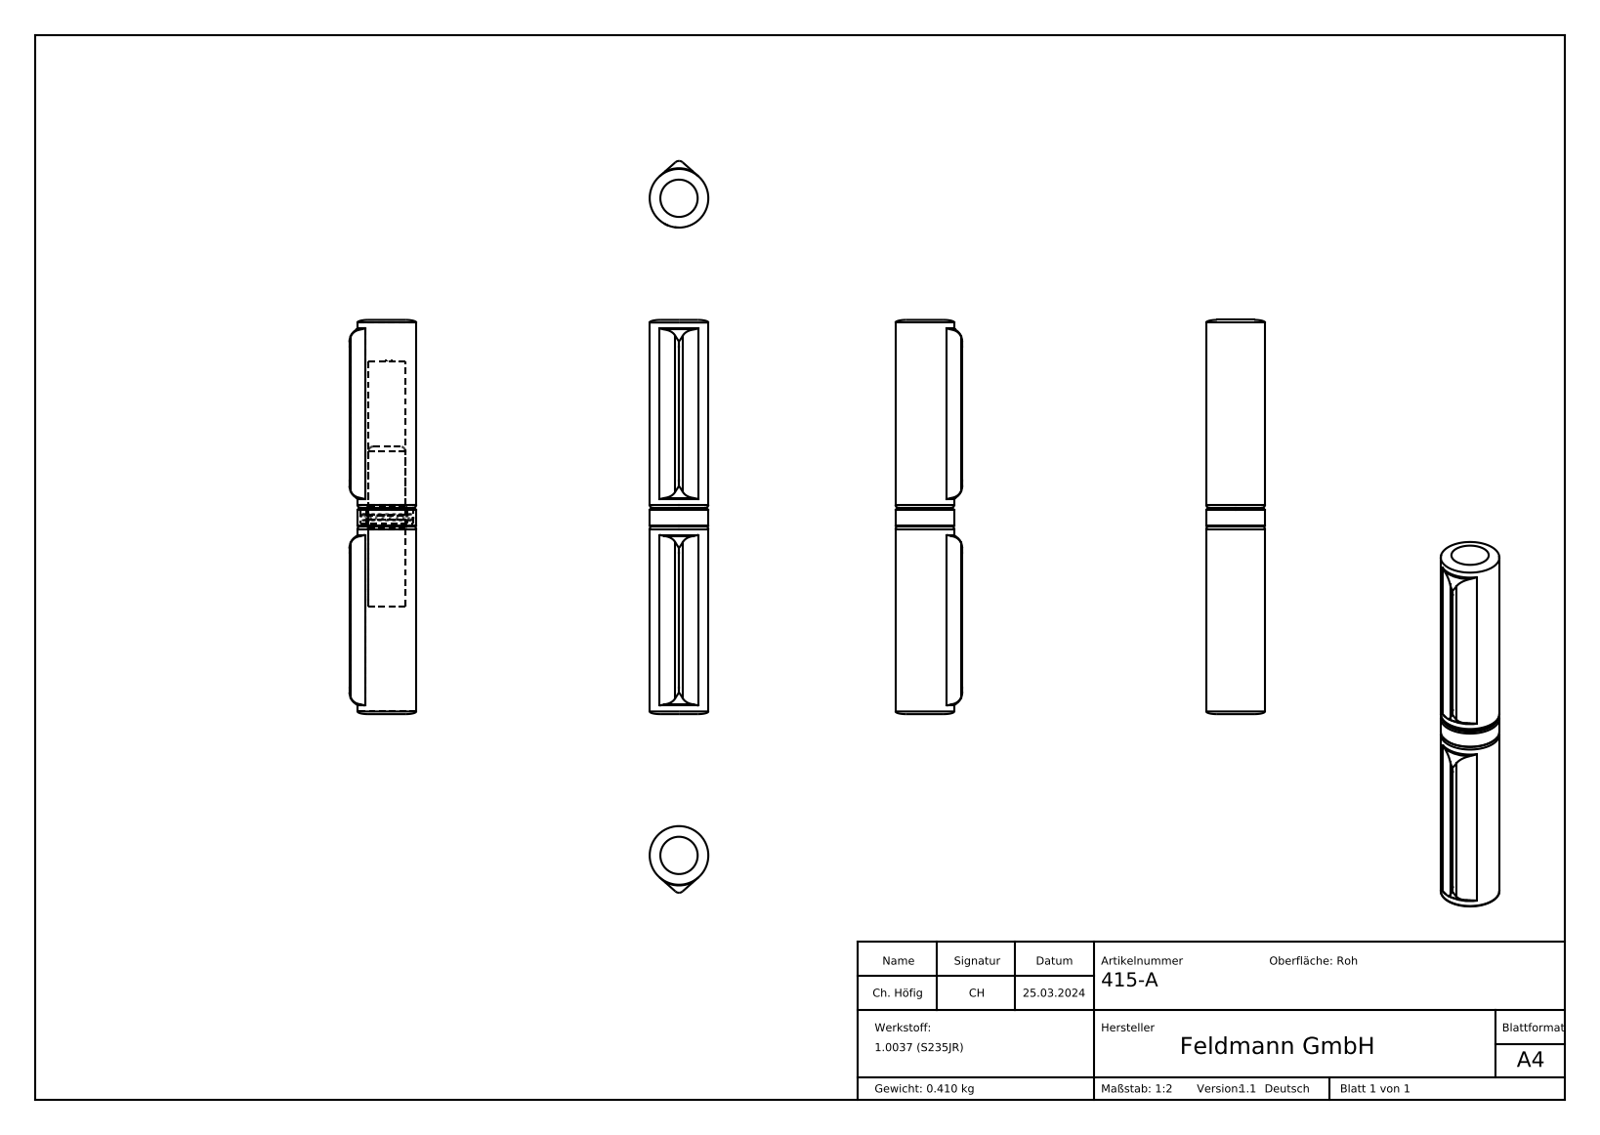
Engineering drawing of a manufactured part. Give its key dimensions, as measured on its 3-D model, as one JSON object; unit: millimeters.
{"part_name": "415-A Teil3_415-A Teil3; 415-A; 415-A Teil2_415-A Teil2; 415-A Teil1_415-A Teil1", "step_written_by": "SolidWorks 2018 (CONFIG_CONTROL_DESIGN)", "units": "millimeters", "bodies": {"solids": 23, "faces": 258, "planar": 140, "cylindrical": 19, "other": 99}, "overall_size": [148, 25, 22], "volume_mm3": 52534, "surface_area_mm2": 20122, "round_holes": [[14.1, 1], [14.2, 1], [20, 1]], "round_bosses_or_shafts": [[22, 1], [15.2, 1], [14, 1]], "partial_cylinders_radius": [[2, 2], [14, 1]], "face_to_face_distances": [77.5, 70.5, 71.5, 76.5, 1, 6, 7, 62, 55, 15.5]}
